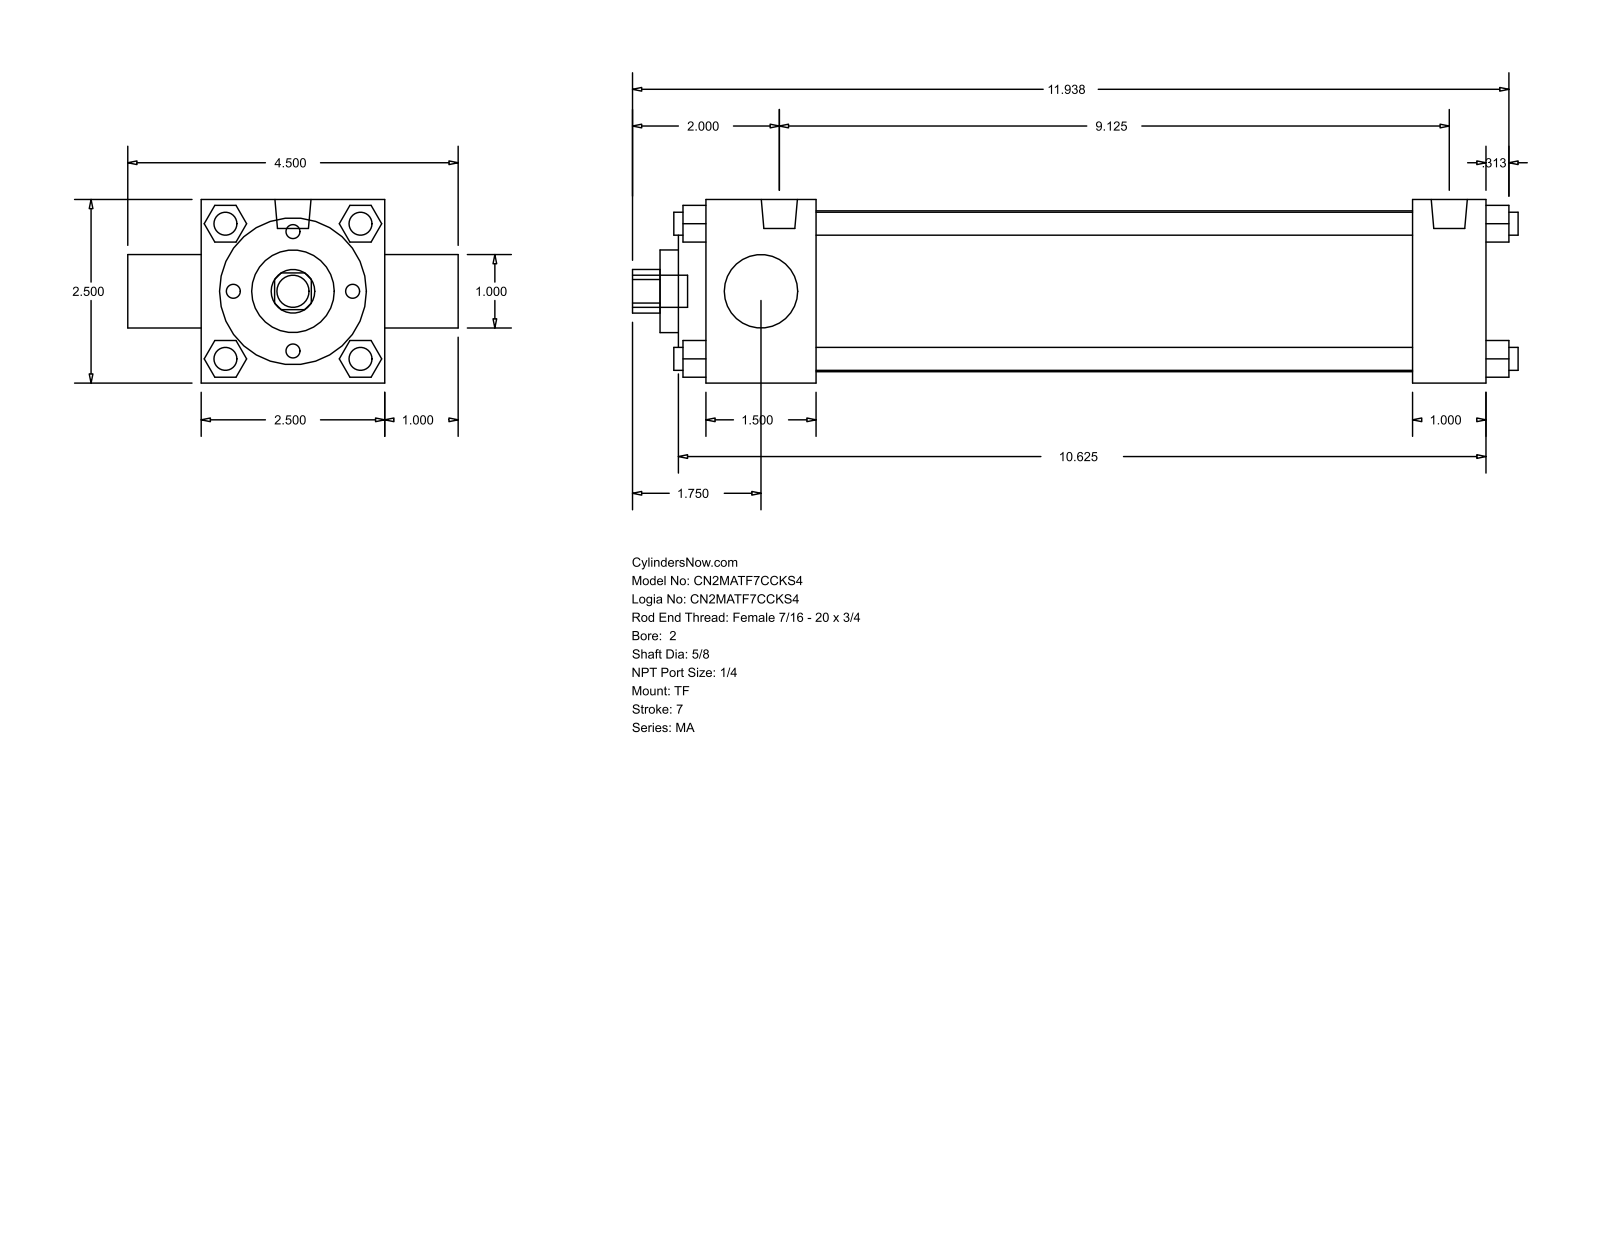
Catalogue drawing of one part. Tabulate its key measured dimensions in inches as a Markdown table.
| quantity | value |
| --- | --- |
| part name | MA_TF__0200_0.625 |
| STEP written by | GSSL Pune (CONFIG_CONTROL_DESIGN) |
| units | inches |
| bodies | 0 solids, 122 faces (93 planar, 29 cylindrical, 0 other) |
| overall size | 12.063 × 4.5 × 2.5 |
| round holes (diameter × count) | 0.625 × 1, 1 × 1, 1.125 × 1, 2 × 1, 2.19 × 1 |
| round bosses / shafts (diameter × count) | 0.313 × 7, 0.492 × 2, 0.437 × 1 |
| partial cylindrical surfaces (radius × count) | 0.297 × 1 |
| main face-to-face distances | 2.5, 1.5, 0.5, 0.375, 10.625, 9.625, 8.125, 9.125, 1, 1.875 |
